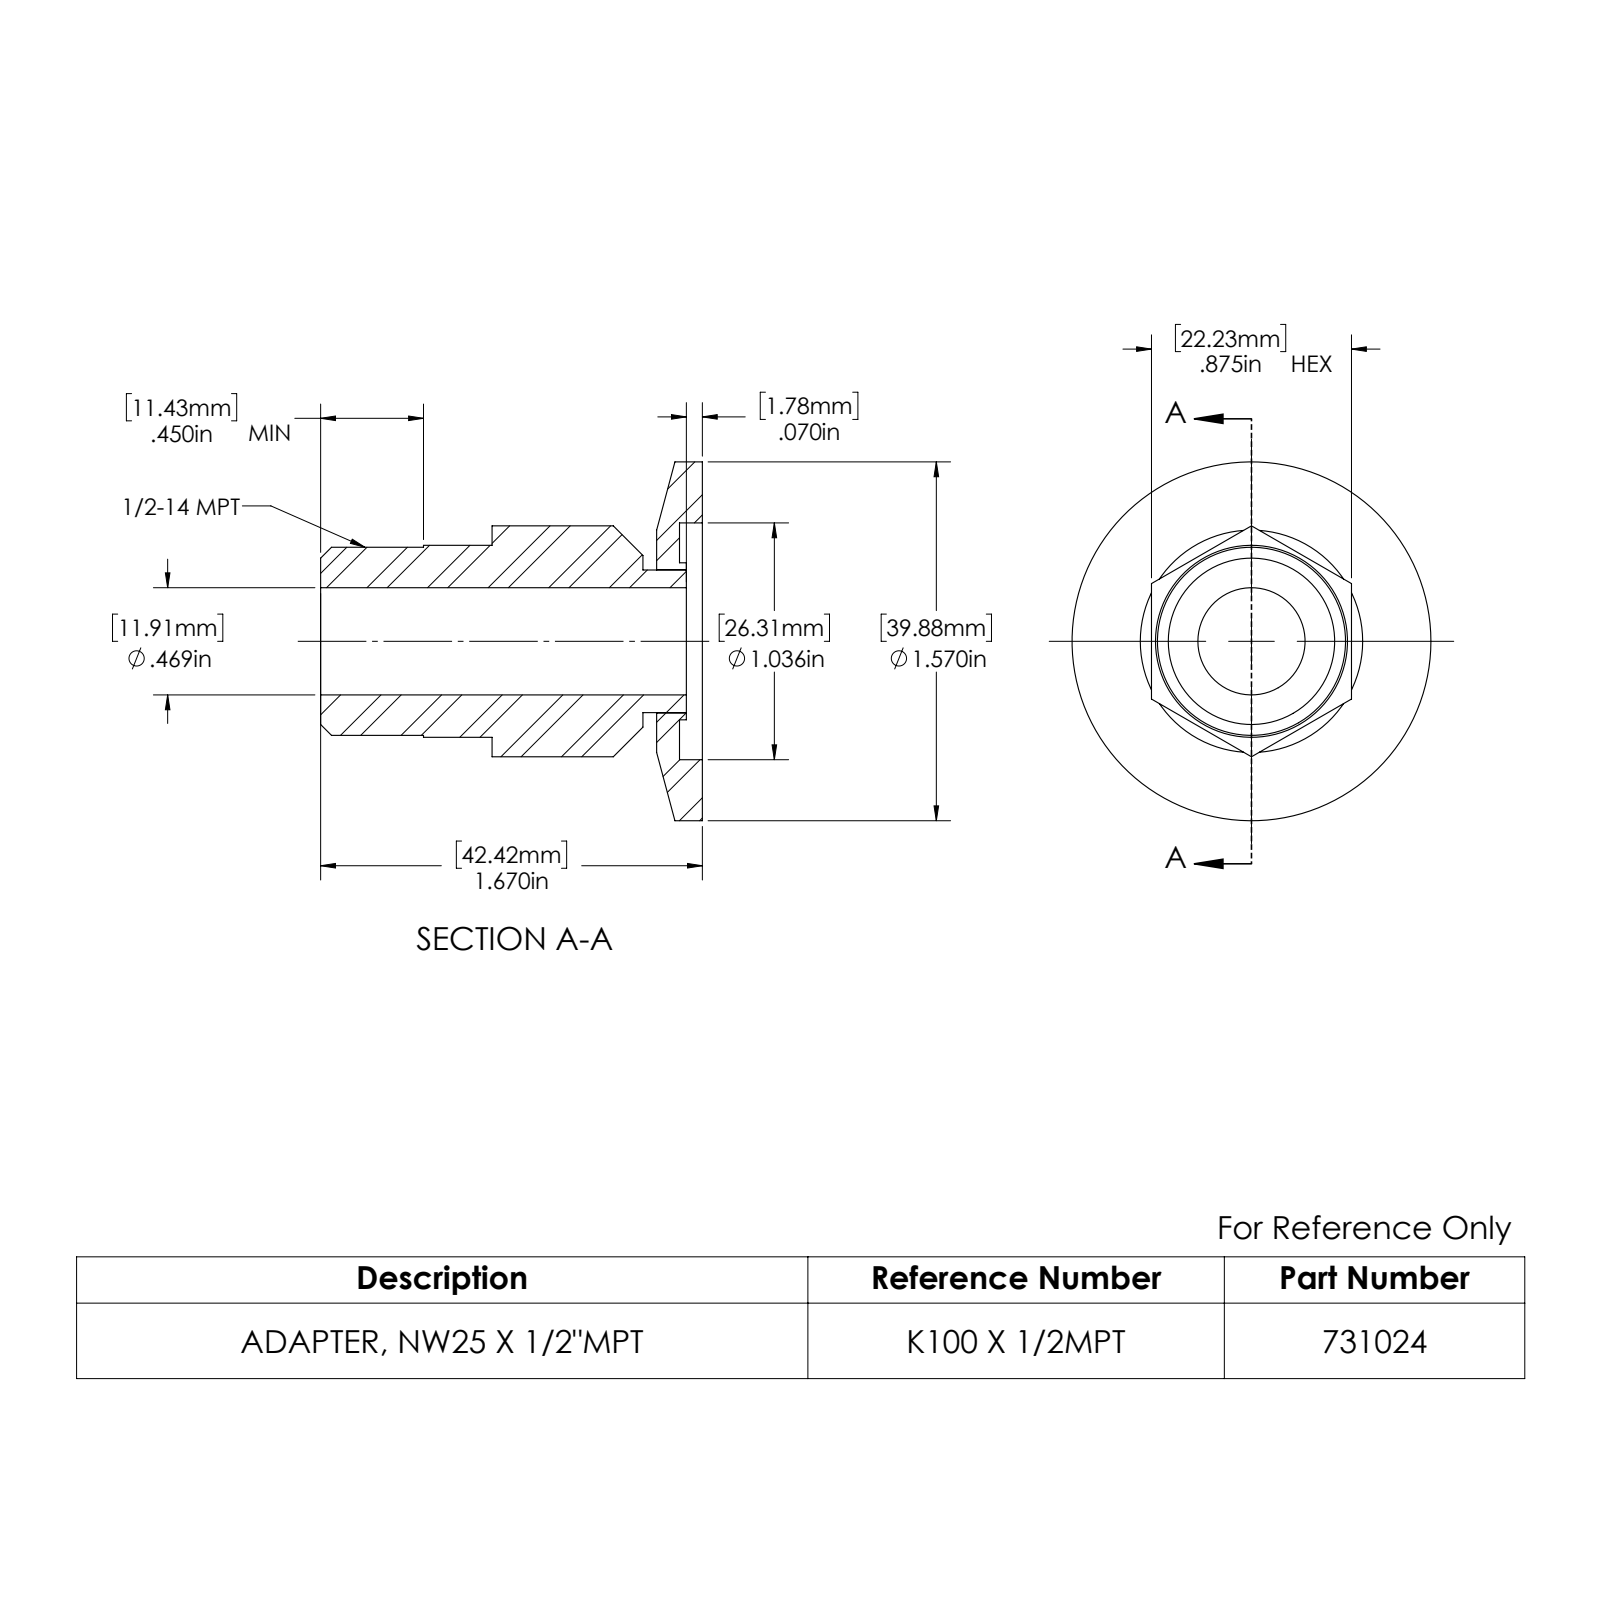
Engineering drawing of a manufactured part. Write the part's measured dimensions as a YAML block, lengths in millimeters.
part_name: "961043; 731024"
step_written_by: "SolidWorks 2022 (AUTOMOTIVE_DESIGN)"
units: millimeters
bodies: {solids: 2, faces: 37, planar: 15, cylindrical: 16, other: 6}
overall_size: [42.4, 39.9, 39.9]
volume: 13700
surface_area: 7716
round_holes:
  - {diameter: 11.9, count: 1}
  - {diameter: 15.9, count: 1}
  - {diameter: 26.3, count: 1}
round_bosses_or_shafts:
  - {diameter: 39.9, count: 1}
  - {diameter: 21.3, count: 1}
  - {diameter: 20.9, count: 1}
  - {diameter: 17.4, count: 1}
  - {diameter: 15.8, count: 1}
face_to_face_distances: [2.5, 22.2, 5.1, 37.3, 39.9, 42.4, 40.6, 3.3, 0.8, 1.8]
